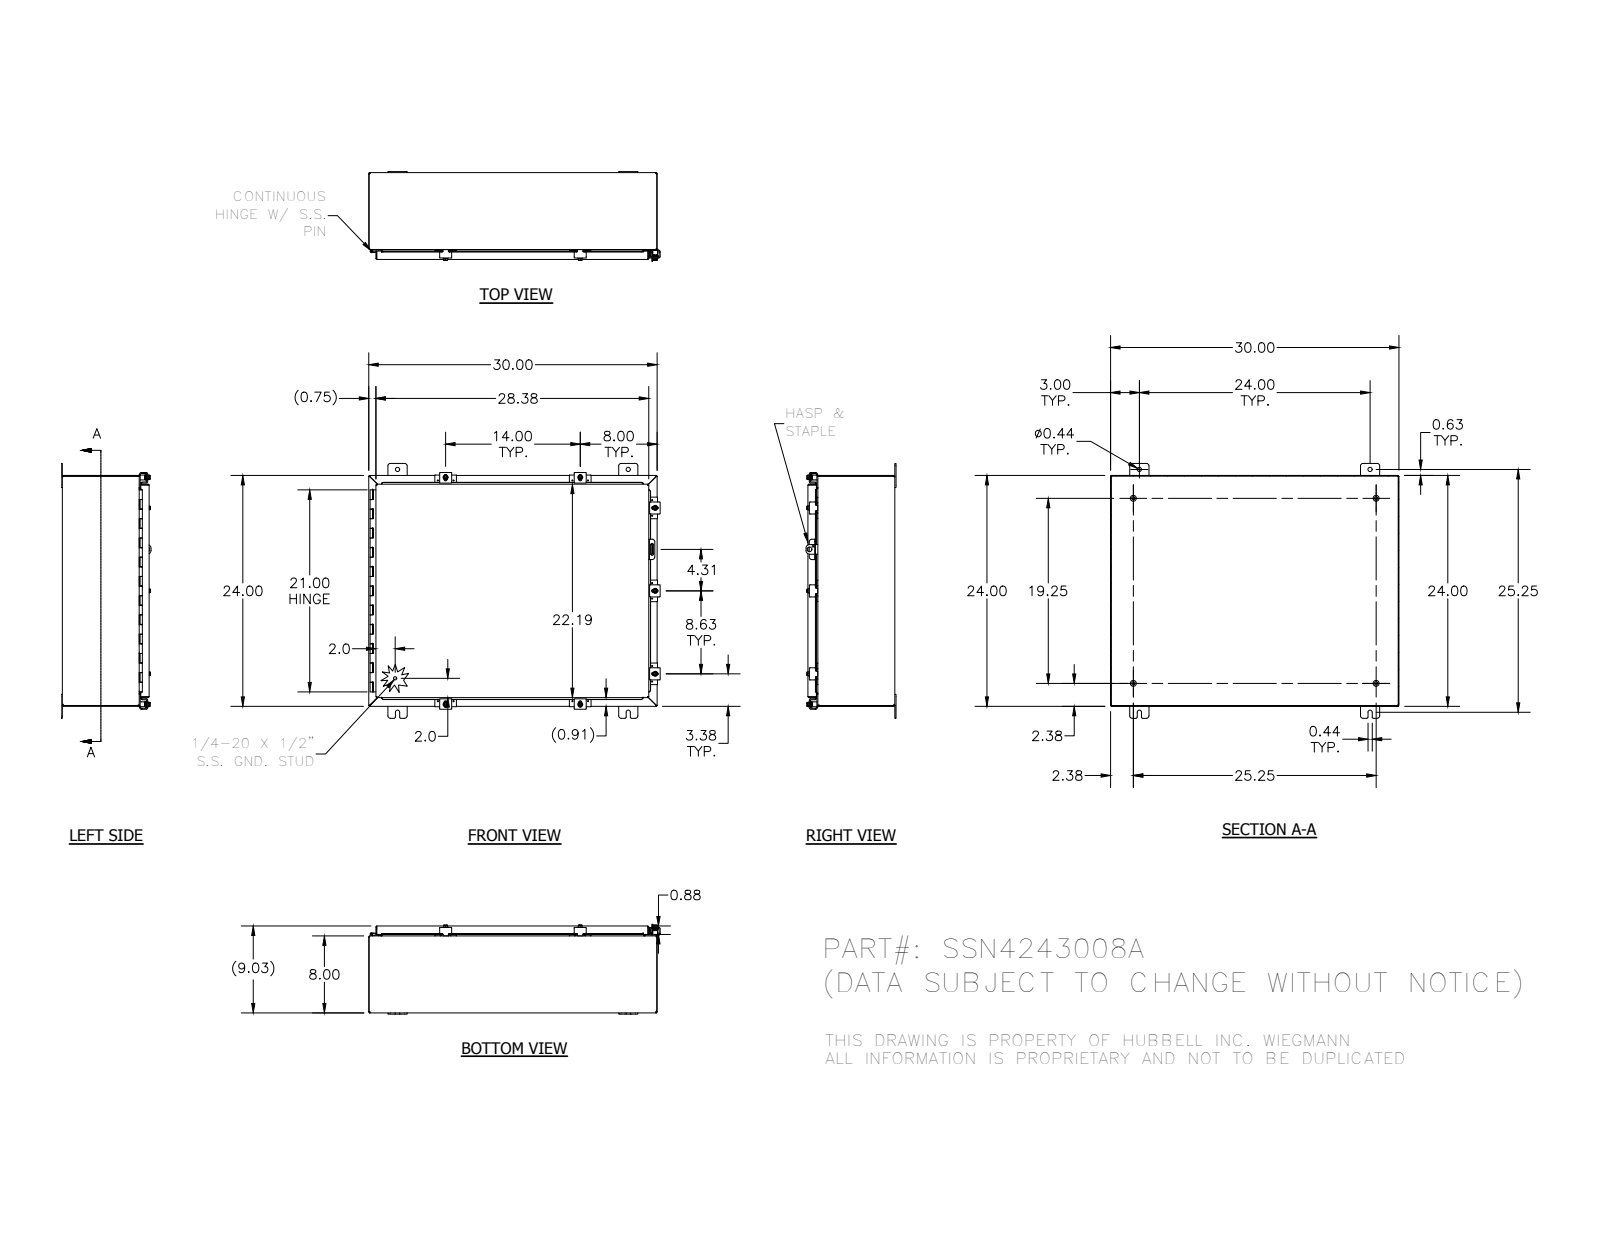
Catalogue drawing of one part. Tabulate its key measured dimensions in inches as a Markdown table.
| quantity | value |
| --- | --- |
| part name | 32912; 30818; SSN4243008ABKP; 30824-3 (+8 more) |
| STEP written by | SolidWorks 2014 (AUTOMOTIVE_DESIGN) |
| units | inches |
| bodies | 52 solids, 2024 faces (782 planar, 875 cylindrical, 367 other) |
| overall size | 30.216 × 26.5 × 9.355 |
| volume | 206.9 in³ |
| surface area | 5 432 in² |
| round holes (diameter × count) | 0.11 × 14, 0.211 × 7, 0.281 × 7, 0.3 × 7, 0.438 × 4, 0.125 × 1, 0.156 × 1, 0.5 × 1 |
| round bosses / shafts (diameter × count) | 0.25 × 9, 0.52 × 7, 0.5 × 7, 0.35 × 7, 0.625 × 4, 0.33 × 4, 0.337 × 1, 0.12 × 1 |
| partial cylindrical surfaces (radius × count) | 0.03 × 83, 0.125 × 37, 0.25 × 33, 0.031 × 23, 0.105 × 23, 0.062 × 18, 0.141 × 14, 0.1 × 10 |
| main face-to-face distances | 0.074, 8.959, 8.885, 9.033, 23.926, 29.926, 7.926, 1.033, 24, 23.852 |
| hole center spacings | 0.876, 23.303, 14, 1.625, 13.191, 14.816, 22.961, 23.018 |
